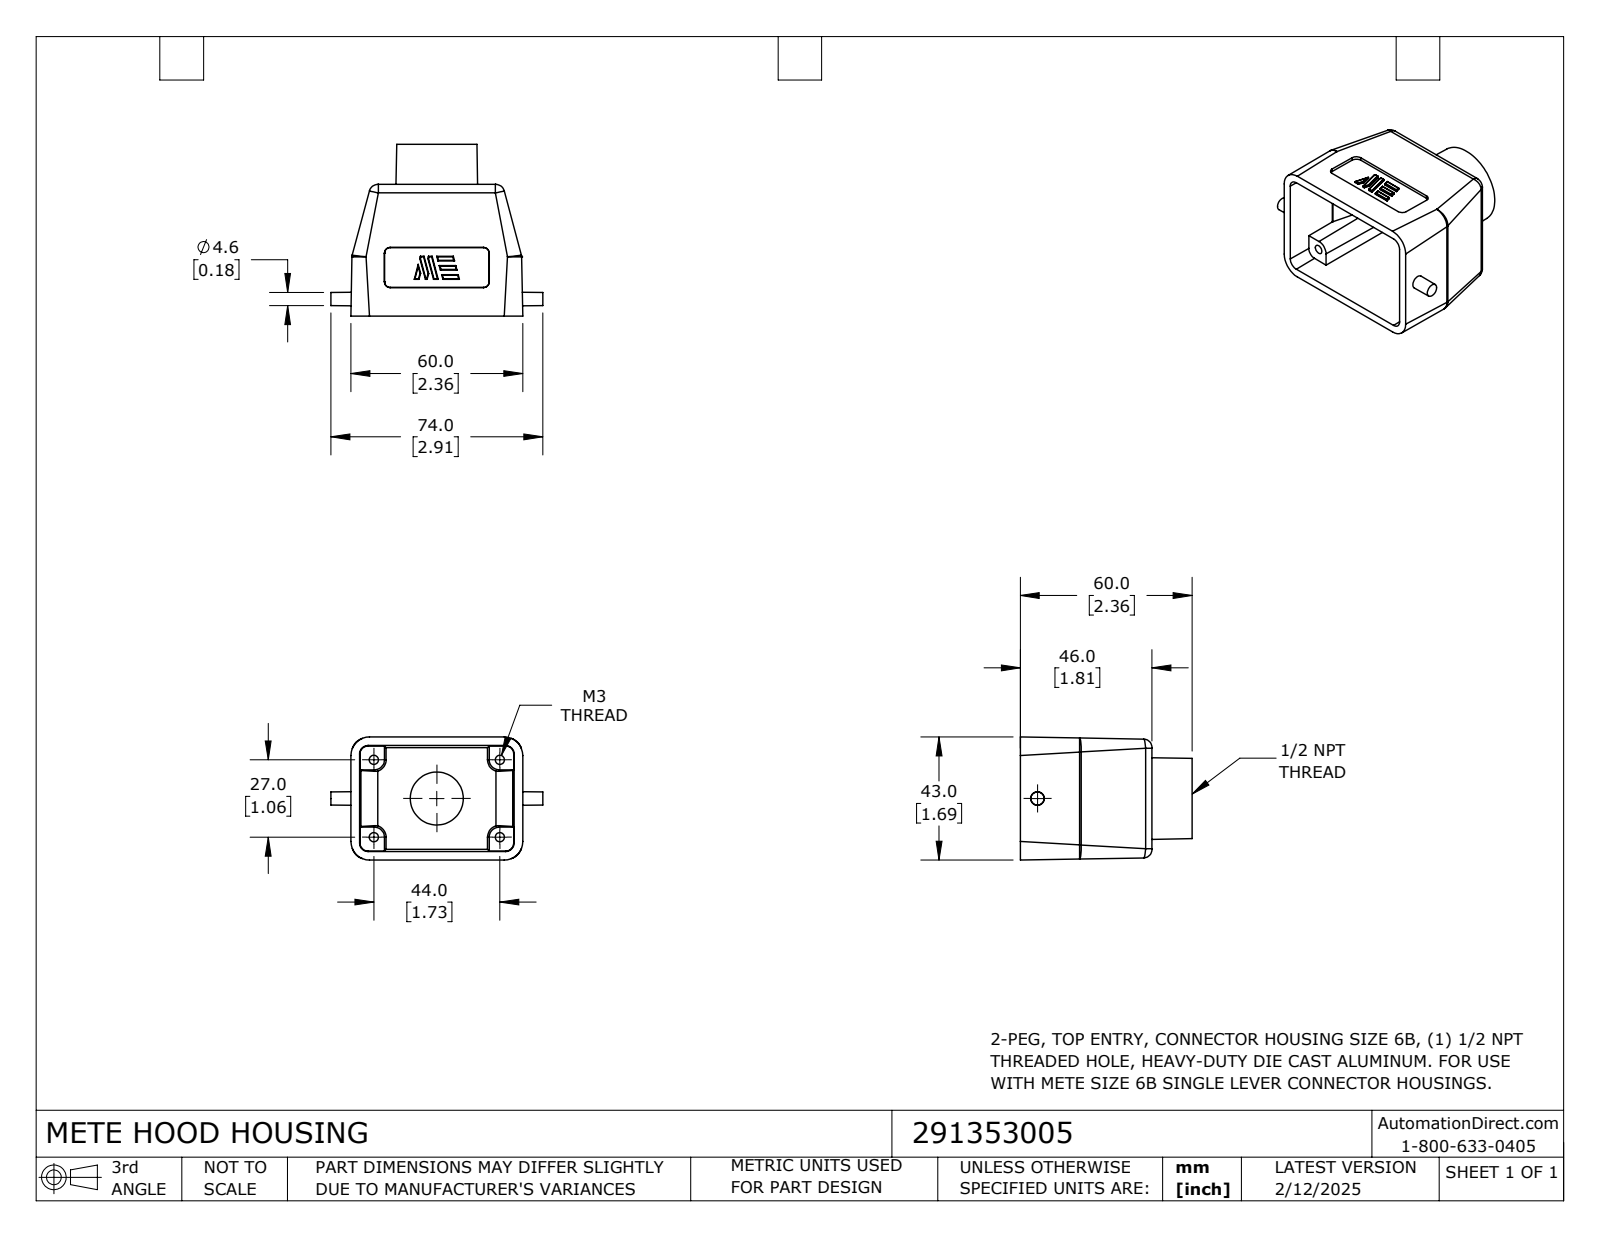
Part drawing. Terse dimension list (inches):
name: 291353005
written by: SolidWorks 2024 (CONFIG_CONTROL_DESIGN)
unit: in
bodies: 1 solid, 227 faces (111 planar, 80 cylindrical, 36 other)
size: 2.913 × 2.362 × 1.693
volume: 2.308 in³; area: 35.19 in²
holes: 4× ⌀0.126, 1× ⌀0.728
rounds: 36× R0.008, 8× R0.079, 4× R0.118, 2× R0.039, 2× R0.098
face distances: 0.118, 0.041, 0.077, 0.455, 0.337, 1.693, 1.811, 0.406, 0.329, 0.447
hole spacings: 1.016, 1.063, 1.732, 2.032
